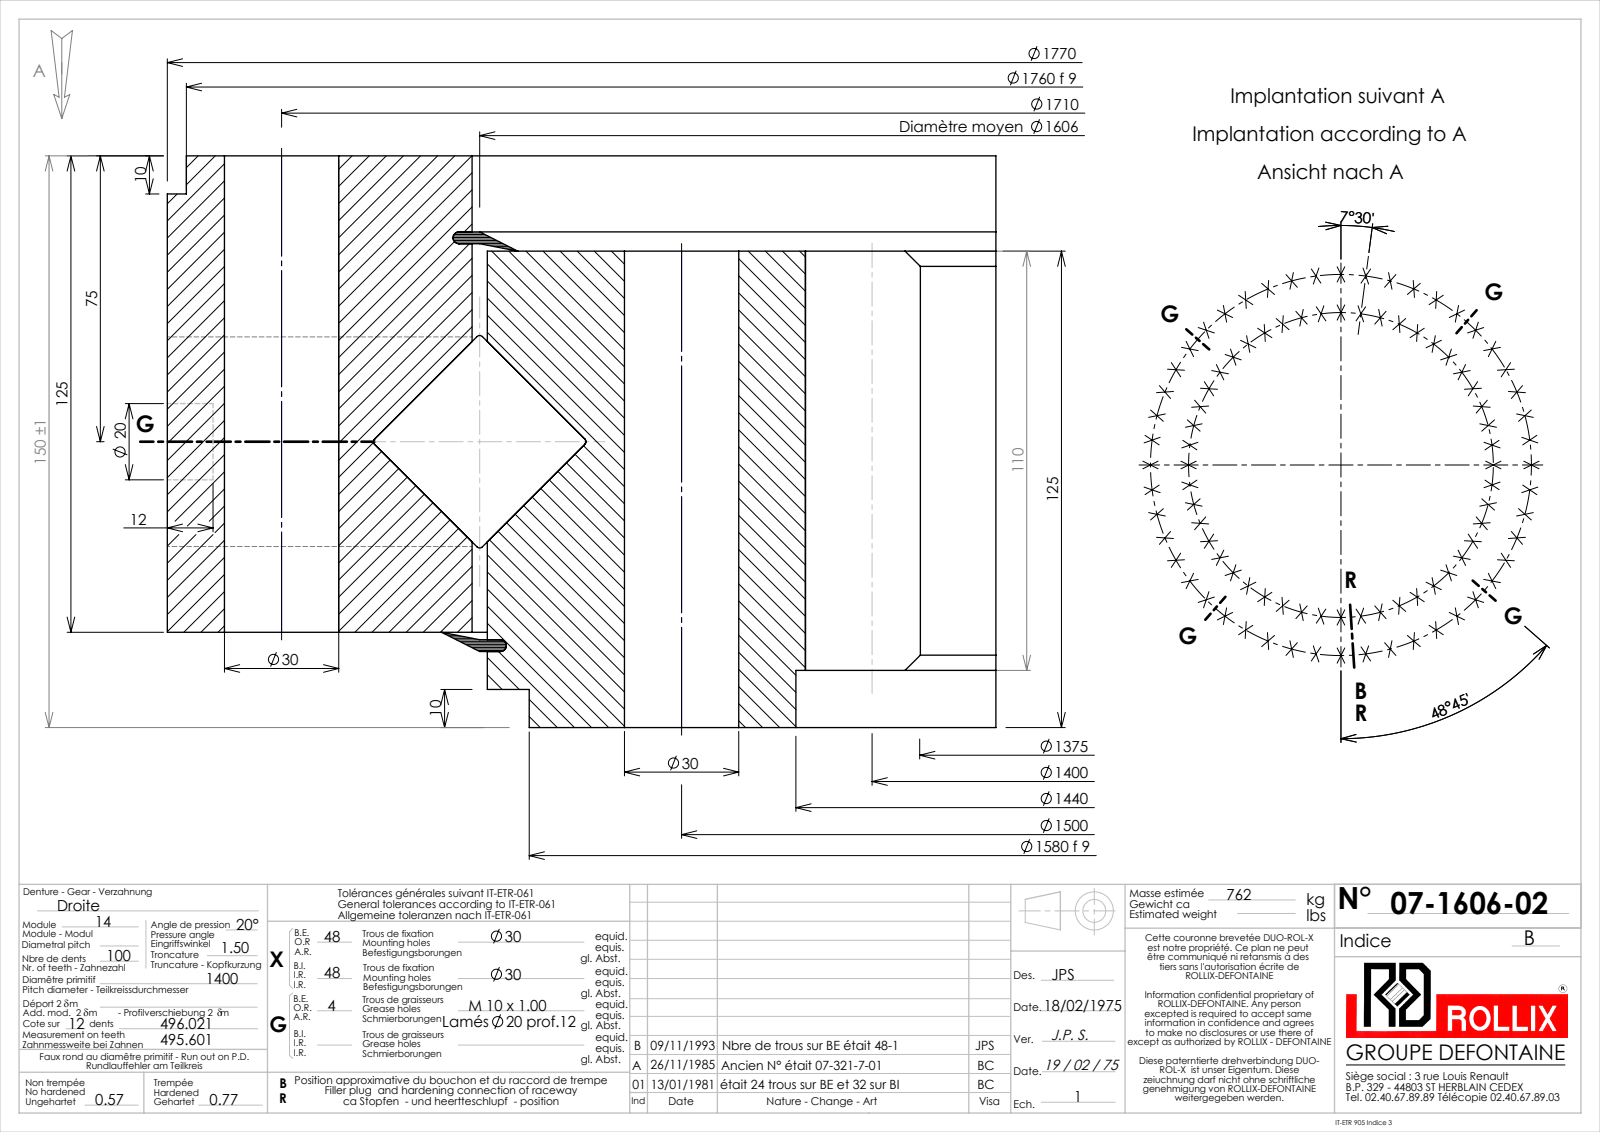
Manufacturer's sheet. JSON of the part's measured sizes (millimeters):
{"part_name": "07-1606-02", "step_written_by": "SolidWorks 2016 (CONFIG_CONTROL_DESIGN)", "units": "millimeters", "bodies": {"solids": 5, "faces": 893, "planar": 221, "cylindrical": 431, "other": 241}, "overall_size": [1770, 1770, 150], "volume_mm3": 94570000, "surface_area_mm2": 6432000, "round_holes": [[30, 96], [9, 4], [20, 4], [1440, 1], [1610, 1]], "round_bosses_or_shafts": [[1770, 1], [1760, 1], [1602, 1], [1580, 1], [40, 1]], "partial_cylinders_radius": [[687.5, 1], [717.5, 1]], "face_to_face_distances": [125, 25, 100, 150, 10, 15, 23.05, 126.95, 1.95, 101.95], "hole_center_spacings": [750, 195.79, 913.14, 388.23, 98.1, 98.11, 292.63, 292.64]}
